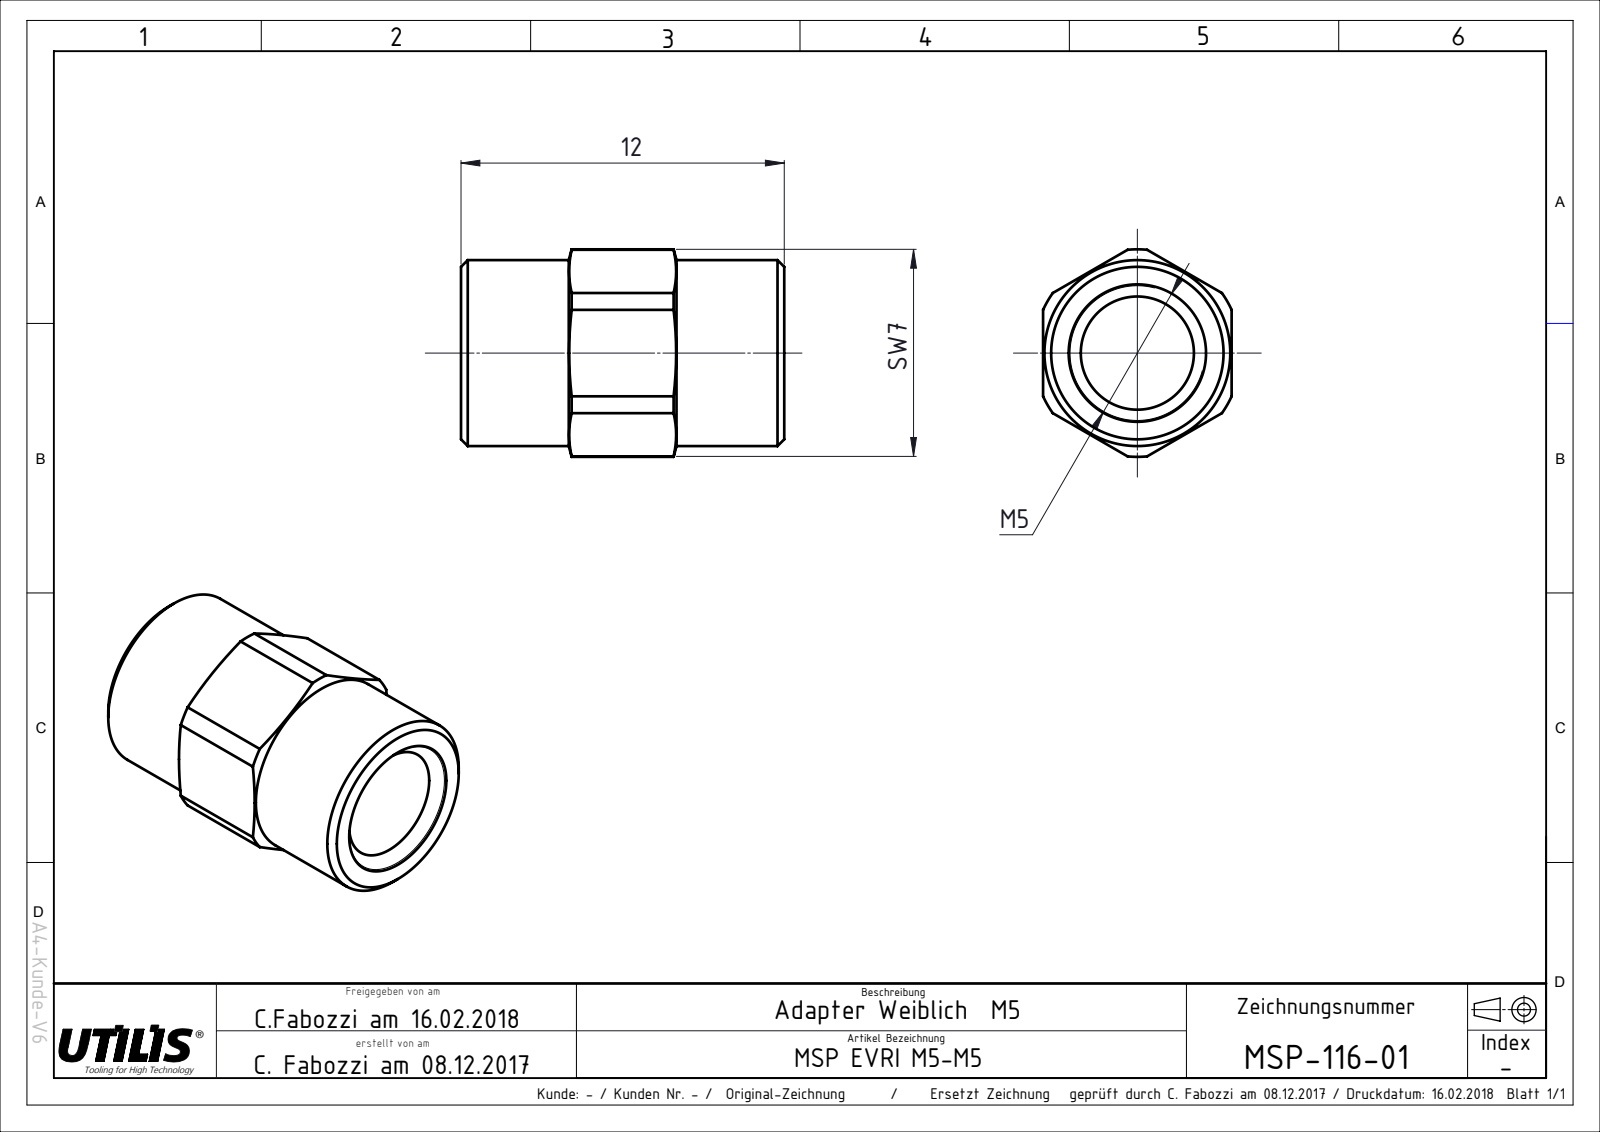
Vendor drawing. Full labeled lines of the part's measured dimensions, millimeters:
Part name (STEP PRODUCT): MSP-116-01
STEP written by: SolidWorks 2017 (AUTOMOTIVE_DESIGN)
Units: millimetres
Bodies: 1 solid, 32 faces (8 planar, 12 cylindrical, 12 other)
Overall size (bounding box): 12 × 7.7 × 7
Volume: 296 mm³ · Surface area: 467 mm²
Round holes (diameter × count): ⌀4.2 ×1
Round bosses / shafts (diameter × count): ⌀6.9 ×1
Partial cylindrical surfaces — rounded edges, fillets, slot ends (radius × count): R3.85 ×1
Main face-to-face distances: 7, 12
